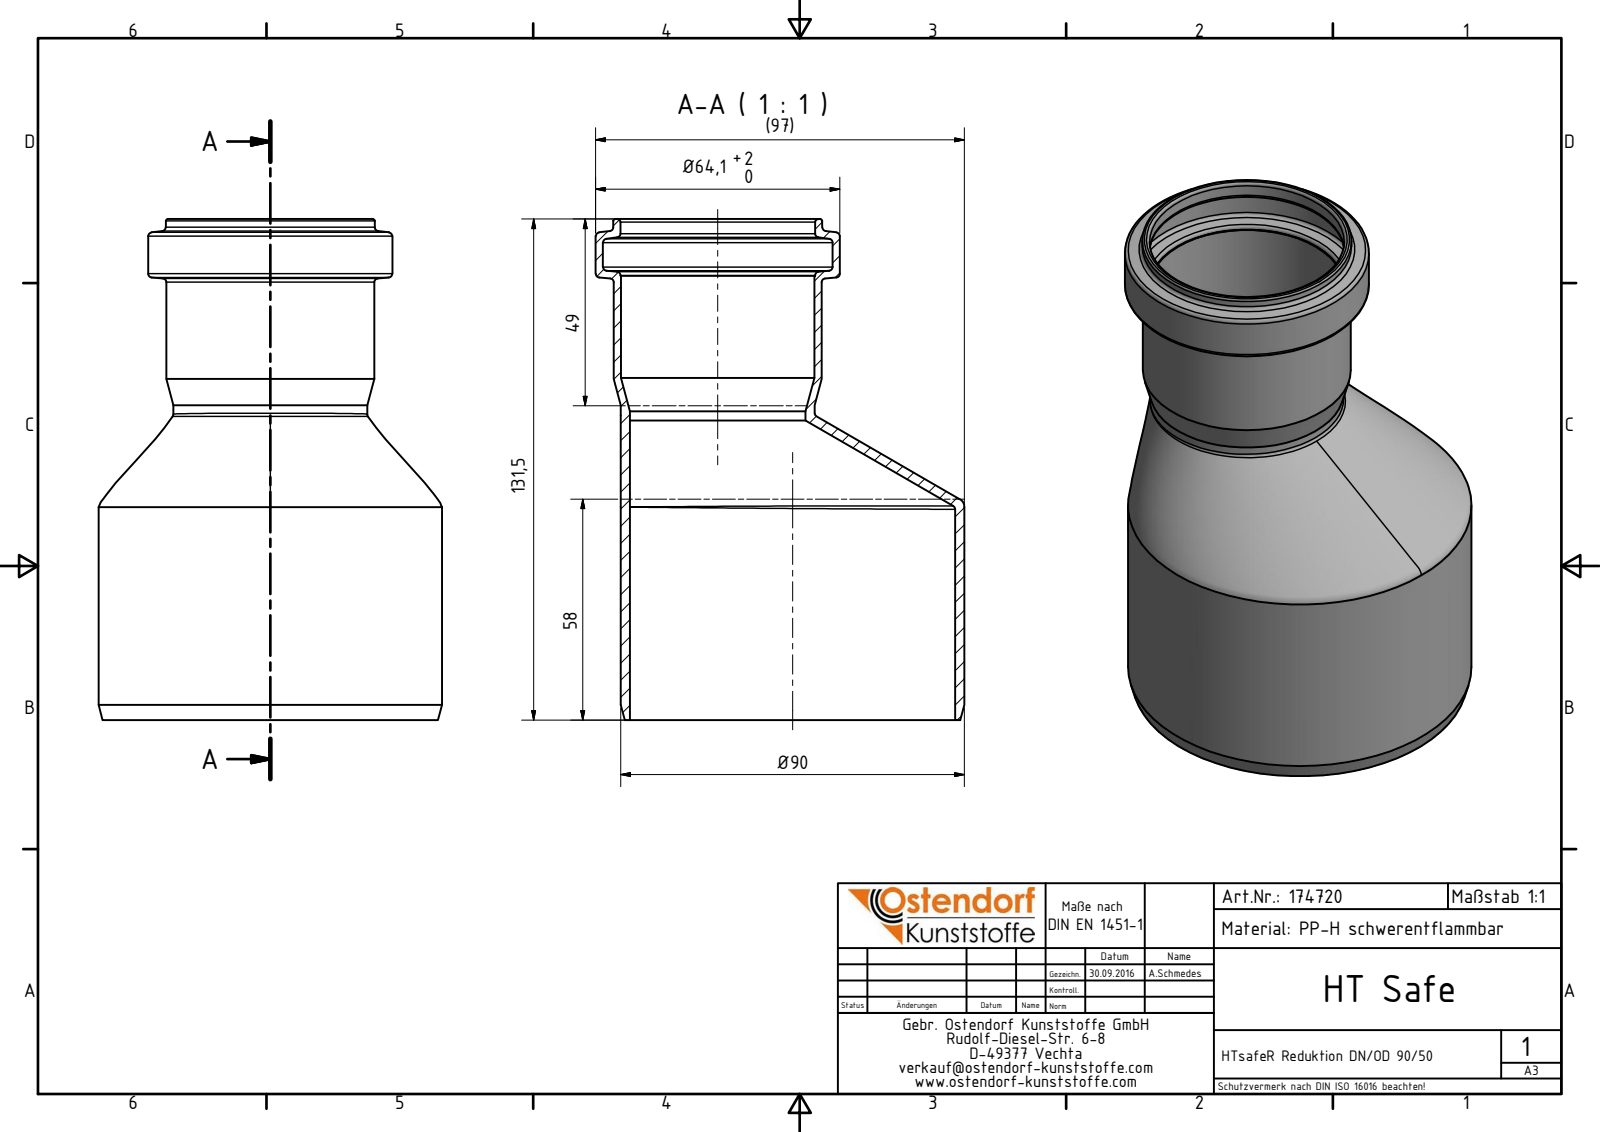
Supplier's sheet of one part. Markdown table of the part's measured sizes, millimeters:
| quantity | value |
| --- | --- |
| part name | 174720 HTsafeR DN_OD 90_50 |
| STEP written by | Autodesk Inventor 2016 (AUTOMOTIVE_DESIGN) |
| units | millimeters |
| bodies | 1 solid, 35 faces (3 planar, 11 cylindrical, 21 other) |
| overall size | 131.5 × 96.8 × 90.2 |
| volume | 73 212 mm³ |
| surface area | 65 833 mm² |
| round holes (diameter × count) | 46.1 × 1, 50.8 × 1, 51.1 × 1, 60.3 × 1, 85.4 × 1 |
| round bosses / shafts (diameter × count) | 90.2 × 1, 64.1 × 1, 54.9 × 1, 54.6 × 1, 50.9 × 1 |
| main face-to-face distances | 131.5, 116.6, 14.9 |
| hole center spacings | 19.65 |
